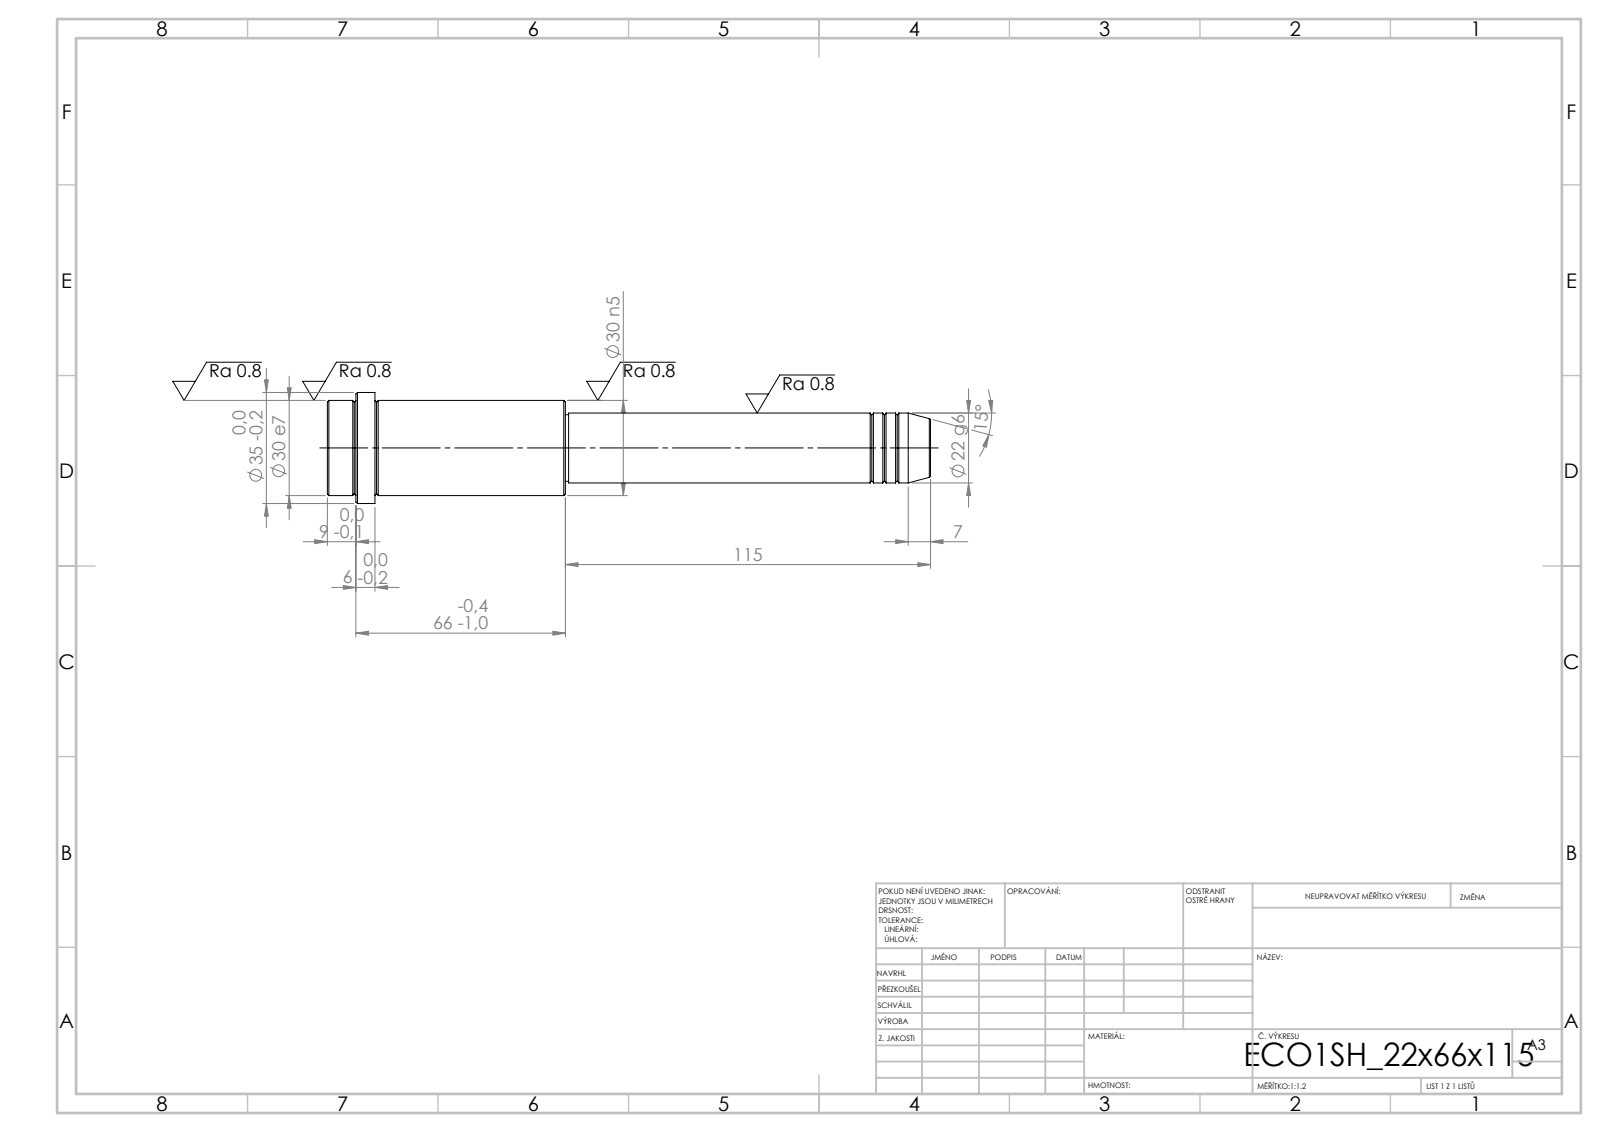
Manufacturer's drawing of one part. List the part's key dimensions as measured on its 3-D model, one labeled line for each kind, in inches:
STEP written by: SolidWorks 2019 (CONFIG_CONTROL_DESIGN)
Units: inches
Bodies: 1 solid, 52 faces (6 planar, 16 cylindrical, 30 other)
Overall size (bounding box): 7.48 × 1.378 × 1.378
Volume: 5.956 in³ · Surface area: 26.46 in²
Round bosses / shafts (diameter × count): ⌀1.378 ×1, ⌀1.181 ×1, ⌀0.866 ×1, ⌀0.827 ×1
Main face-to-face distances: 2.953, 2.362, 0.591, 4.528, 6.89, 7.48, 7.126, 2.598, 0.236, 0.354
